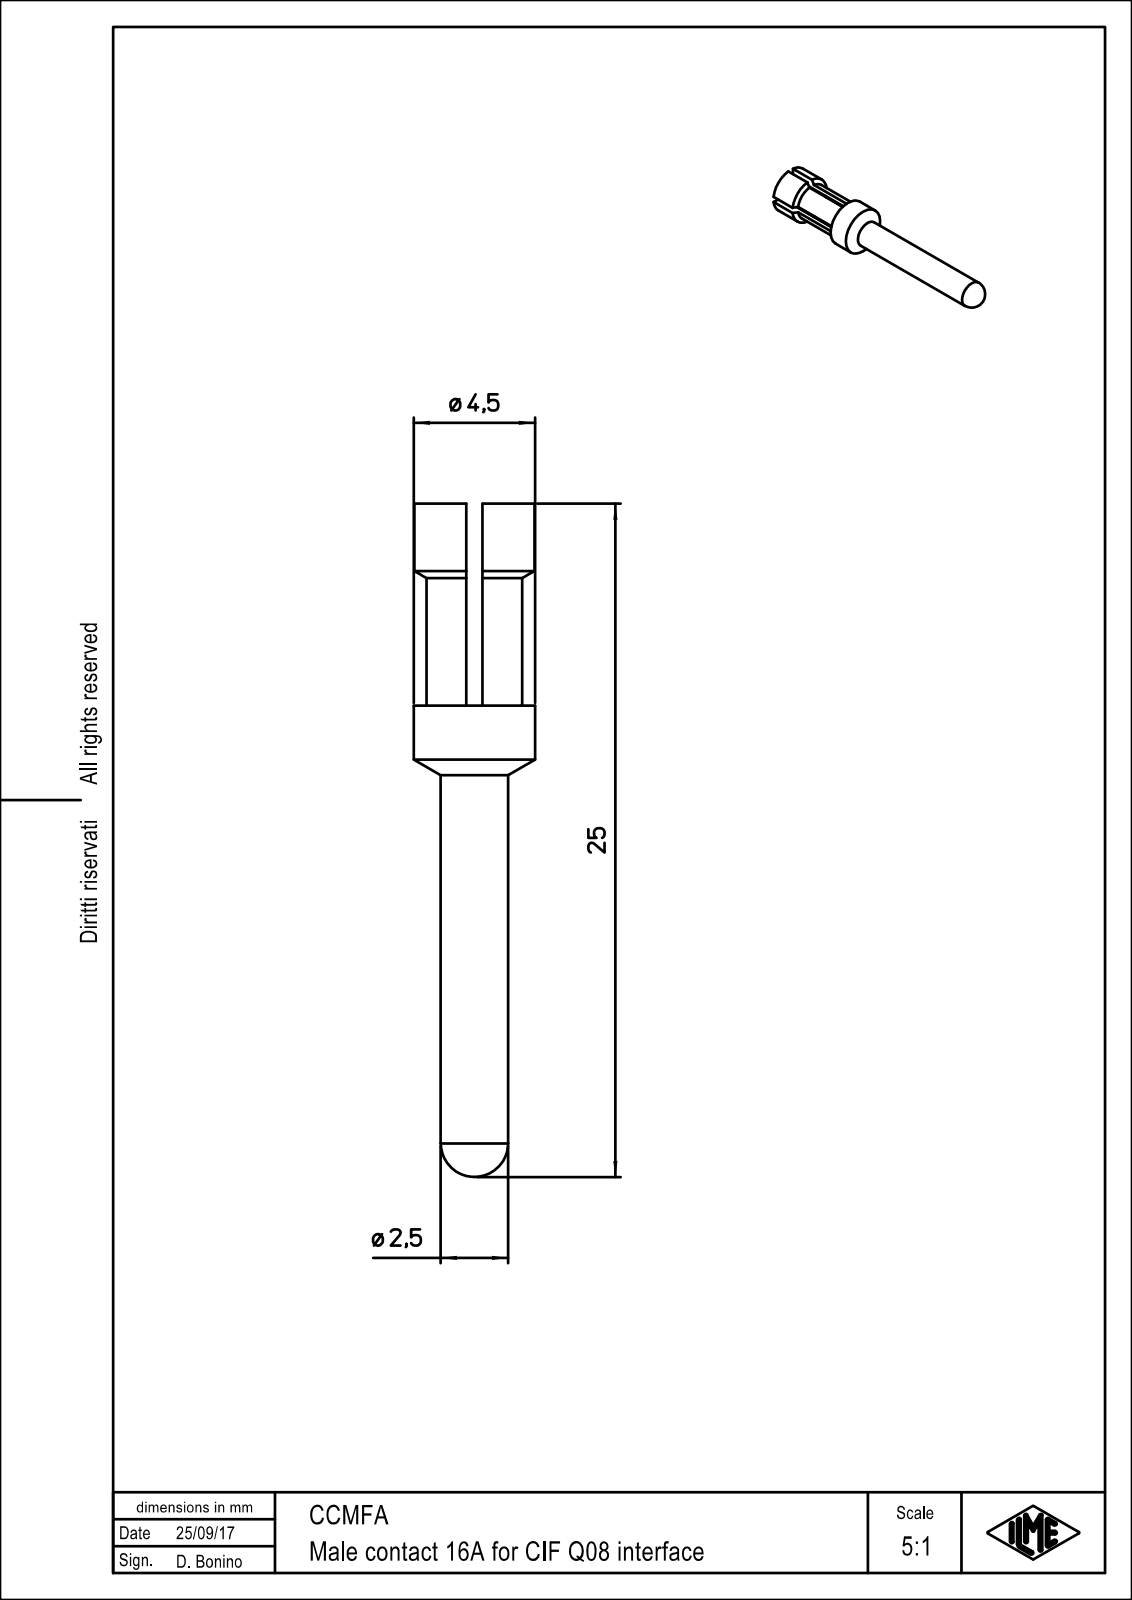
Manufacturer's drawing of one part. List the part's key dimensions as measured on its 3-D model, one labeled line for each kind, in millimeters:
Part name (STEP PRODUCT): CCMFA
STEP written by: PTC Creo Elements/Direct Modeling 19.0B 21-Mar-2015 (C) Parametric Technology GmbH (AUTOMOTIVE_DESIGN)
Units: millimetres
Bodies: 1 solid, 37 faces (13 planar, 16 cylindrical, 8 other)
Overall size (bounding box): 25 × 4.5 × 4.5
Volume: 148 mm³ · Surface area: 339 mm²
Round bosses / shafts (diameter × count): ⌀4.5 ×1, ⌀2.5 ×1
Partial cylindrical surfaces — rounded edges, fillets, slot ends (radius × count): R1.3 ×1, R1.8 ×1
Main face-to-face distances: 0.6, 7.5
